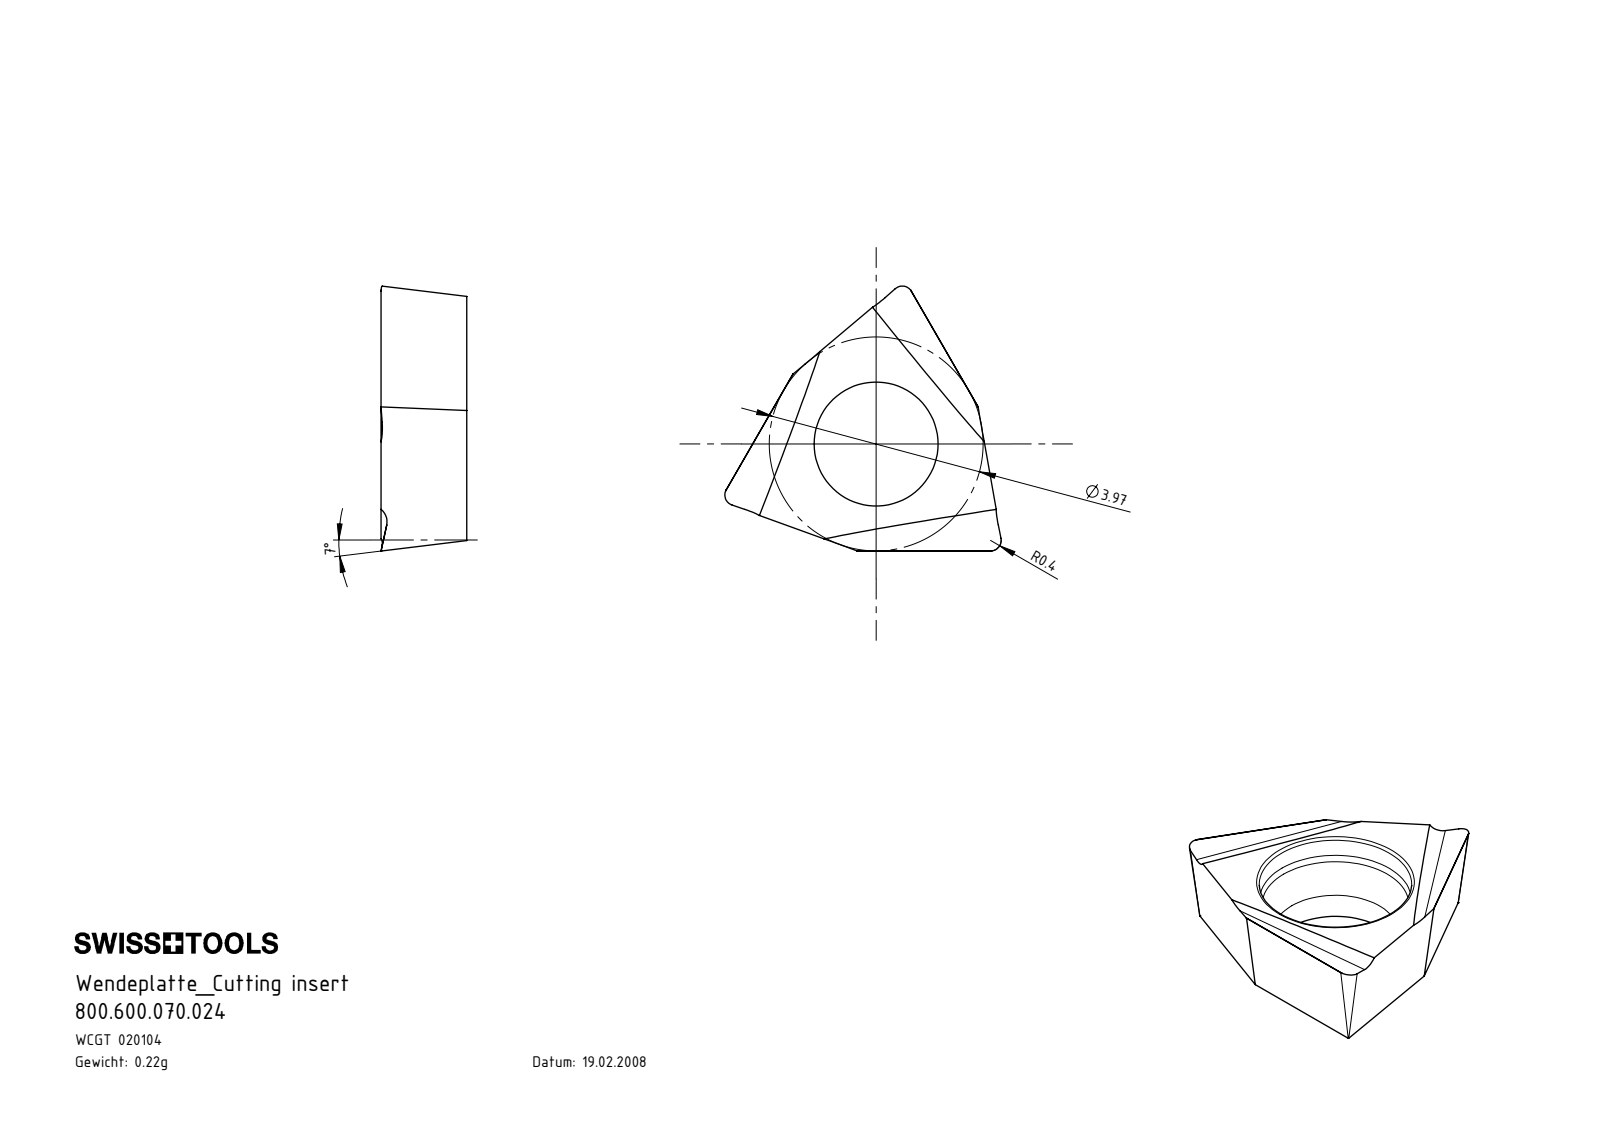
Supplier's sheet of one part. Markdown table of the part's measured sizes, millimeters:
| quantity | value |
| --- | --- |
| part name | 800.600.070.024 |
| STEP written by | SolidWorks 2022 (AUTOMOTIVE_DESIGN) |
| units | millimeters |
| bodies | 1 solid, 31 faces (14 planar, 5 cylindrical, 12 other) |
| overall size | 5.13 × 4.92 × 1.59 |
| volume | 15 mm³ |
| surface area | 56 mm² |
| round holes (diameter × count) | 2.3 × 1 |
| partial cylindrical surfaces (radius × count) | 0.3 × 3 |
| main face-to-face distances | 1.59 |
